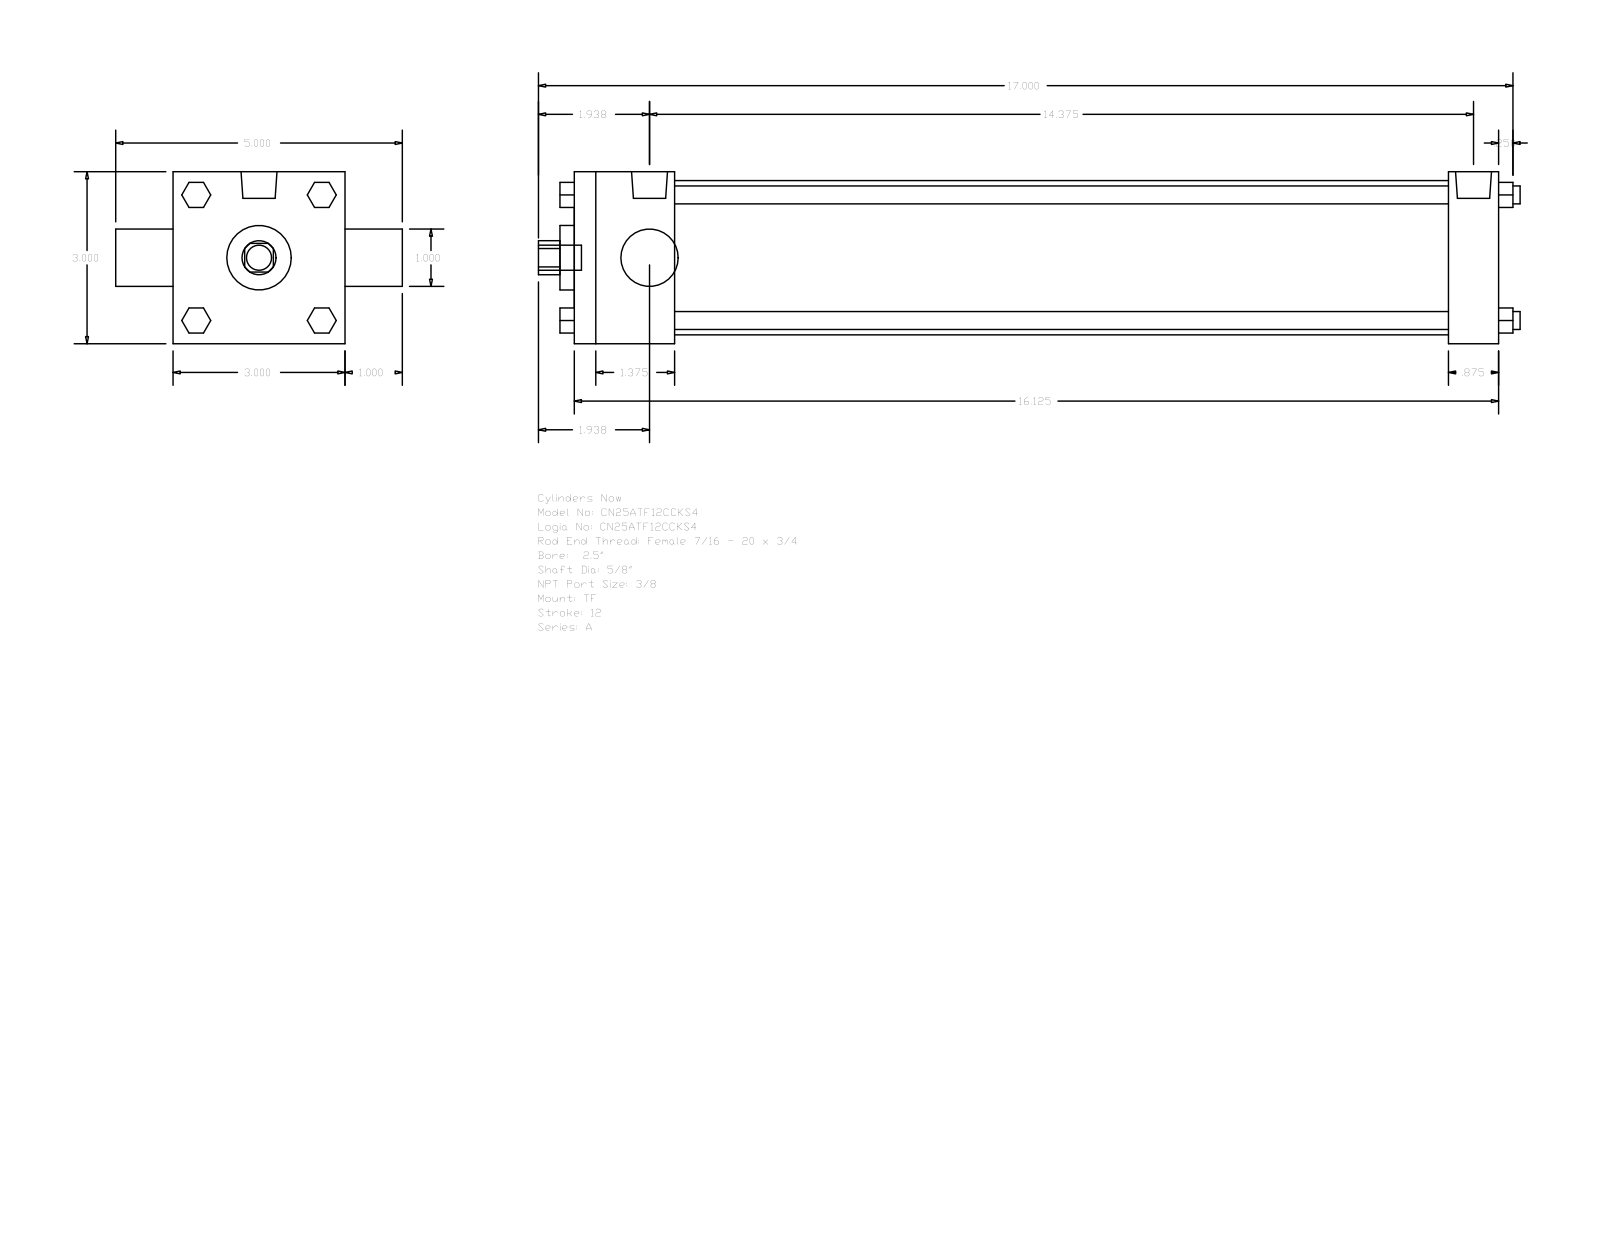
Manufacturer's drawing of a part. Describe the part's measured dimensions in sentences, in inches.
The part is named "A_TF__0250_0.625". Its 3-D file was written by "GSSL Pune (CONFIG_CONTROL_DESIGN)". It is 0 solids with 120 faces: 92 planar, 28 cylindrical and 0 other. Overall it measures 17.125 by 5 by 3 inches. Round holes: 1 of diameter 0.625, 1 of diameter 1, 1 of diameter 1.125, 1 of diameter 2.69. Round bosses or shafts: 4 of diameter 0.313, 3 of diameter 0.219, 2 of diameter 0.627, 1 of diameter 0.437. Partial cylindrical surfaces (rounded edges, fillets, slot ends): 1 of radius 0.297. The main face-to-face distances are 3, 16.125, 1.75, 15.25, 13.5, 14.375, 0.875, 1, 4, 0.25.
